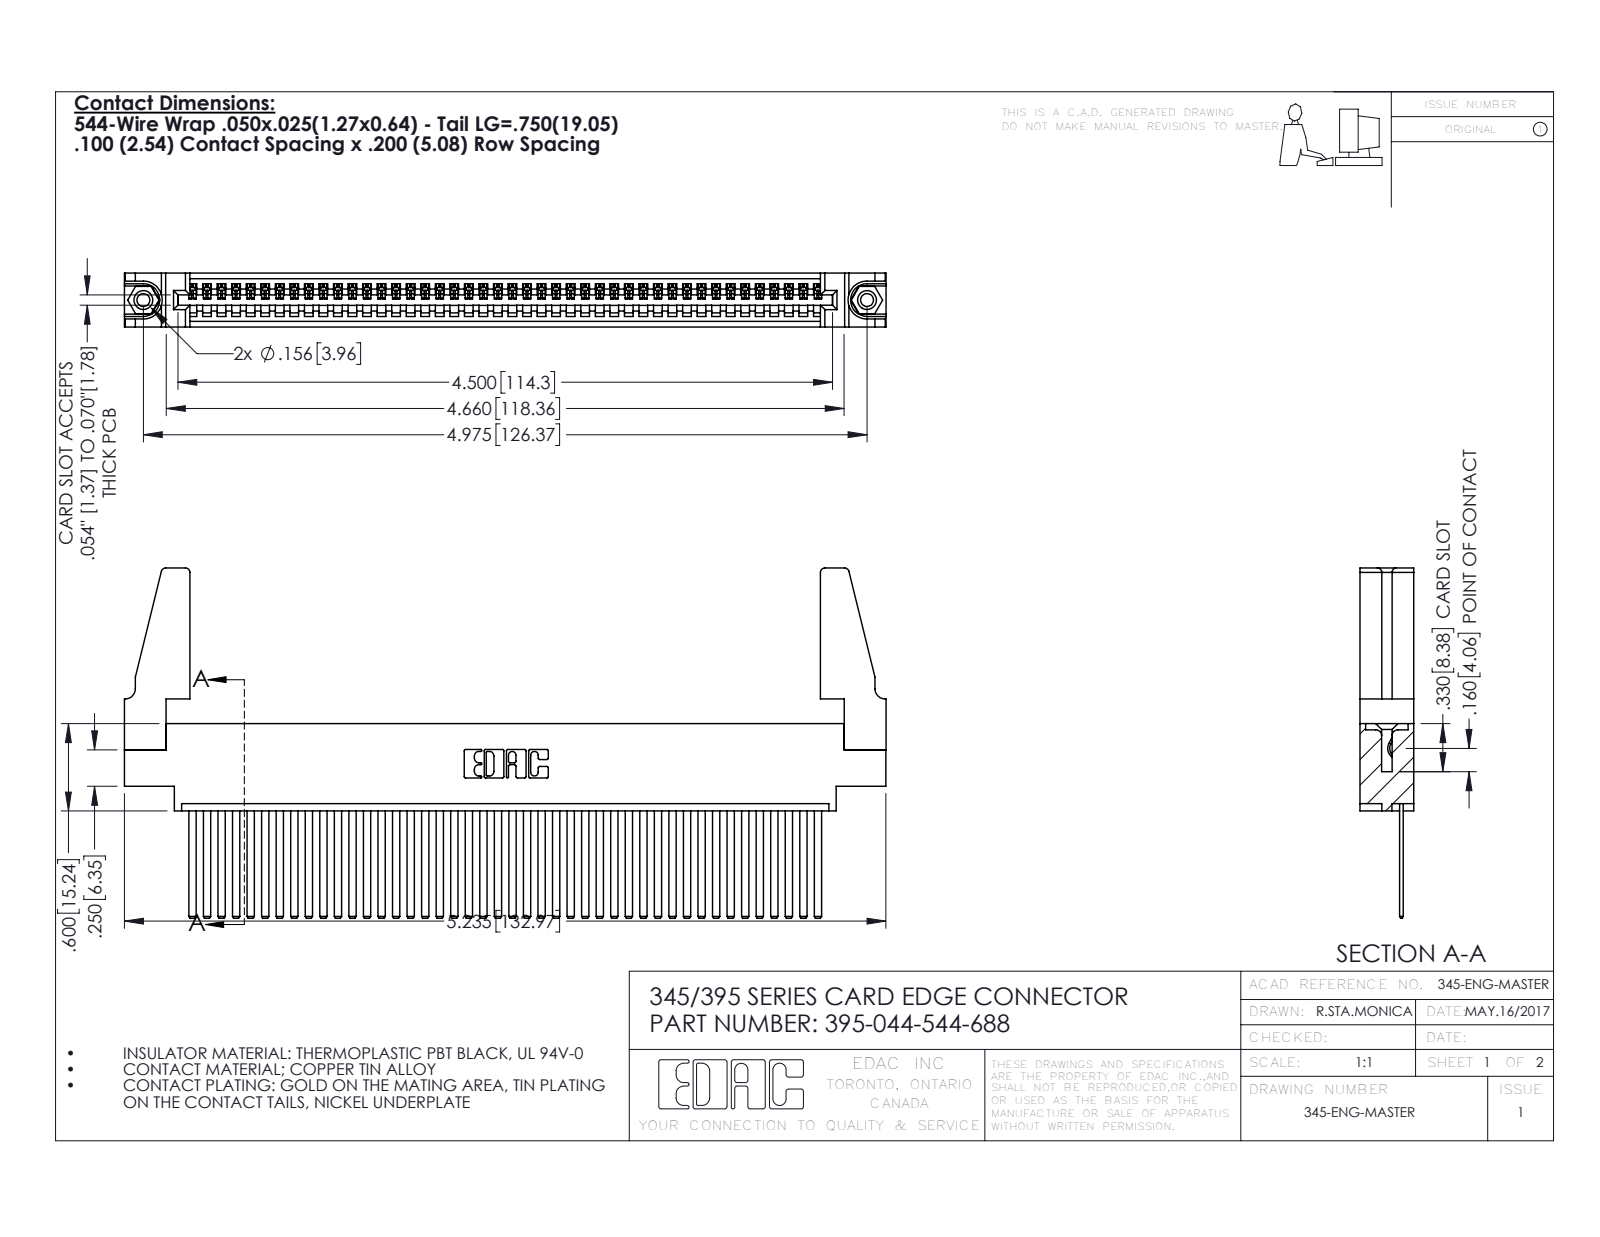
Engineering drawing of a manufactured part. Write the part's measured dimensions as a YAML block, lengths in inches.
part_name: "345 Part_0.170 Offset - 0.156 Dia-TH; 395-044-544-688; 345-250-001_345-250-001-102; 345-292-001_345-293-144 (+1 more)"
step_written_by: "SolidWorks 2016 (CONFIG_CONTROL_DESIGN)"
units: inches
bodies: {solids: 49, faces: 2542, planar: 1740, cylindrical: 786, other: 16}
overall_size: [5.236, 2.407, 0.37]
volume: 0.995
surface_area: 34.33
round_holes:
  - {diameter: 0.089, count: 2}
  - {diameter: 0.125, count: 2}
  - {diameter: 0.156, count: 2}
  - {diameter: 0.064, count: 1}
round_bosses_or_shafts:
  - {diameter: 0.155, count: 2}
partial_cylinders:
  - {radius: 0.006, count: 88}
  - {radius: 0.01, count: 22}
  - {radius: 0.03, count: 8}
  - {radius: 0.007, count: 6}
  - {radius: 0.031, count: 6}
  - {radius: 0.026, count: 3}
  - {radius: 0.031, count: 2}
  - {radius: 0.04, count: 2}
face_to_face_distances: [0.072, 0.298, 0.37, 0.098, 0.272, 0.025, 0.2, 0.225, 0.175, 0.149]
hole_center_spacings: [0.27, 4.739, 4.975]
